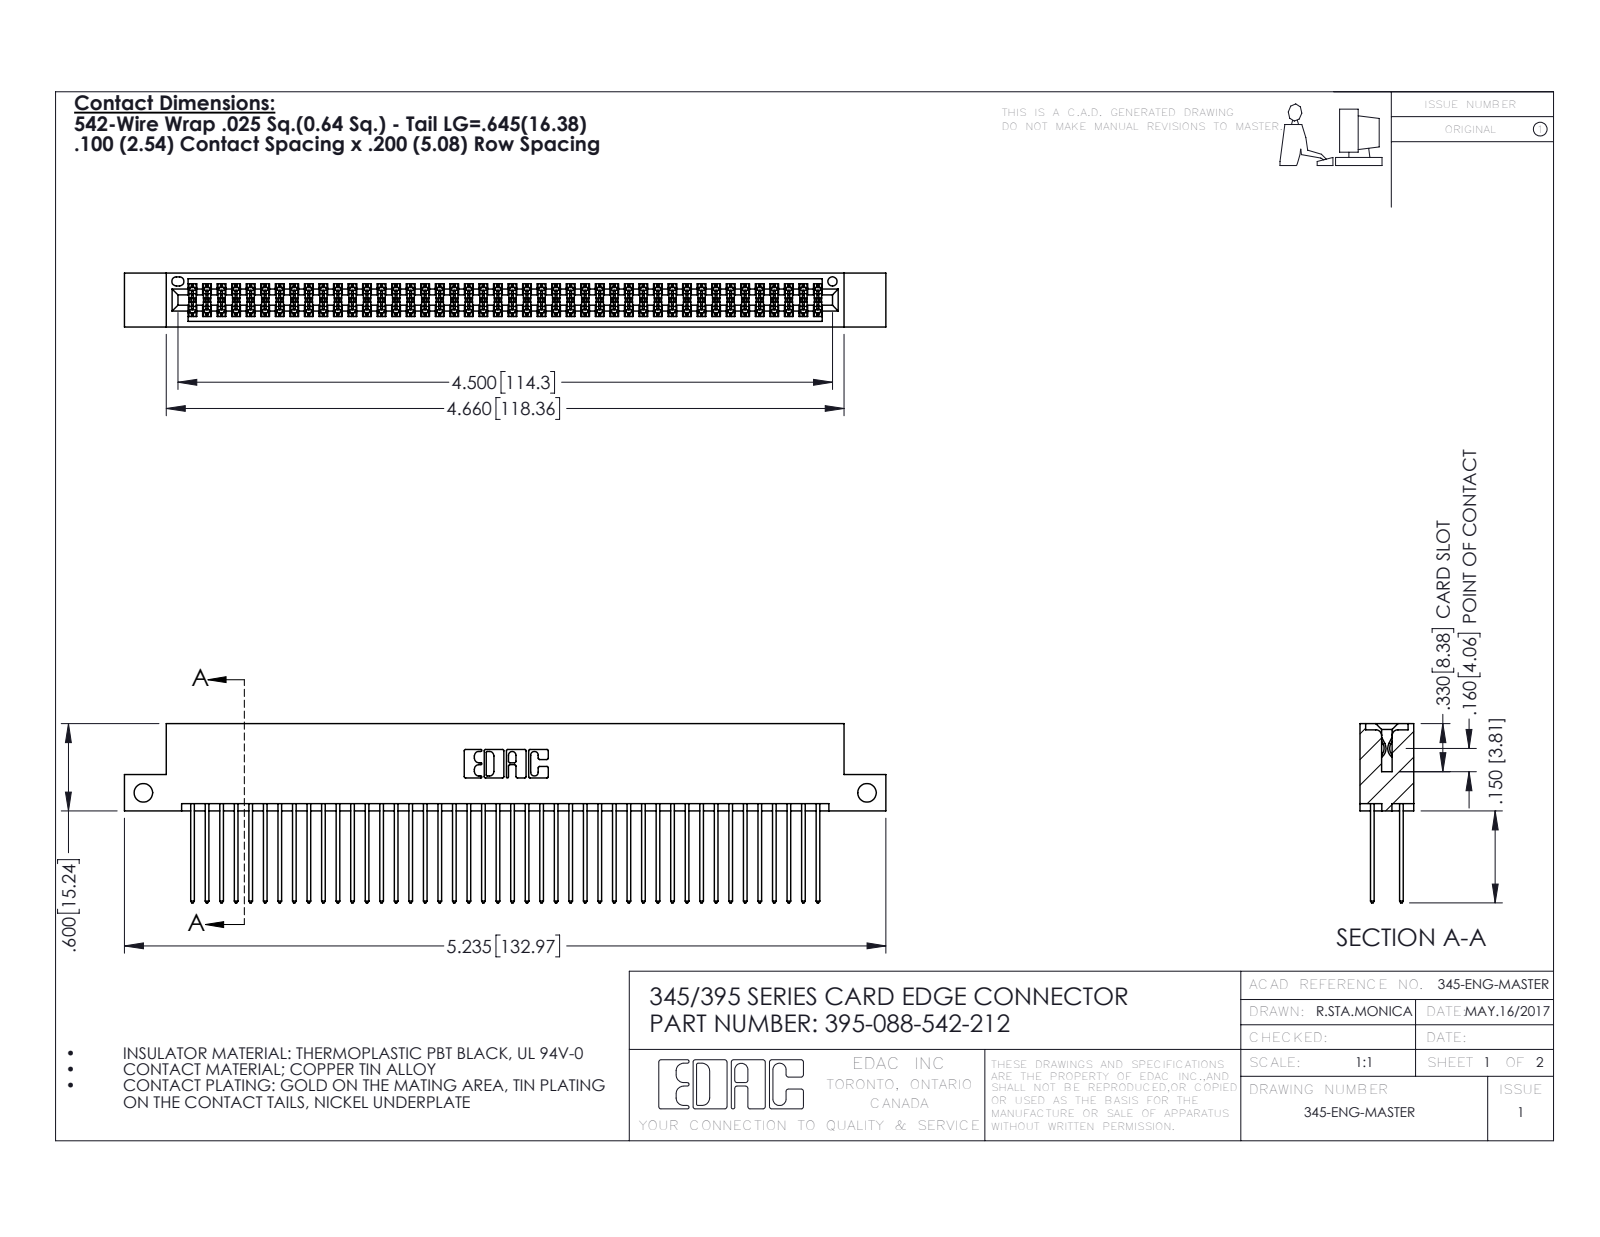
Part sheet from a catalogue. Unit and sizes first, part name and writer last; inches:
Units: inches
Overall size (bounding box): 5.235 × 1.232 × 0.37
Round holes (diameter × count): ⌀0.128 ×2, ⌀0.064 ×1
Partial cylindrical surfaces — rounded edges, fillets, slot ends (radius × count): R0.006 ×132, R0.01 ×88, R0.01 ×22, R0.007 ×6, R0.031 ×6, R0.026 ×3, R0.014 ×2, R0.019 ×2
Main face-to-face distances: 0.298, 0.072, 0.2, 0.098, 0.272, 0.025, 0.225, 0.37, 0.175, 0.149
Hole centre spacings: 4.975
Volume: 0.809 in³ · Surface area: 33.2 in²
Bodies: 89 solids, 4526 faces (2984 planar, 1542 cylindrical, 0 other)
Part name (STEP PRODUCT): 345 Part_Flush Mounting Lugs - Side Mount; 345-292-001_345-293-142; 395-088-542-212
STEP written by: SolidWorks 2016 (CONFIG_CONTROL_DESIGN)
